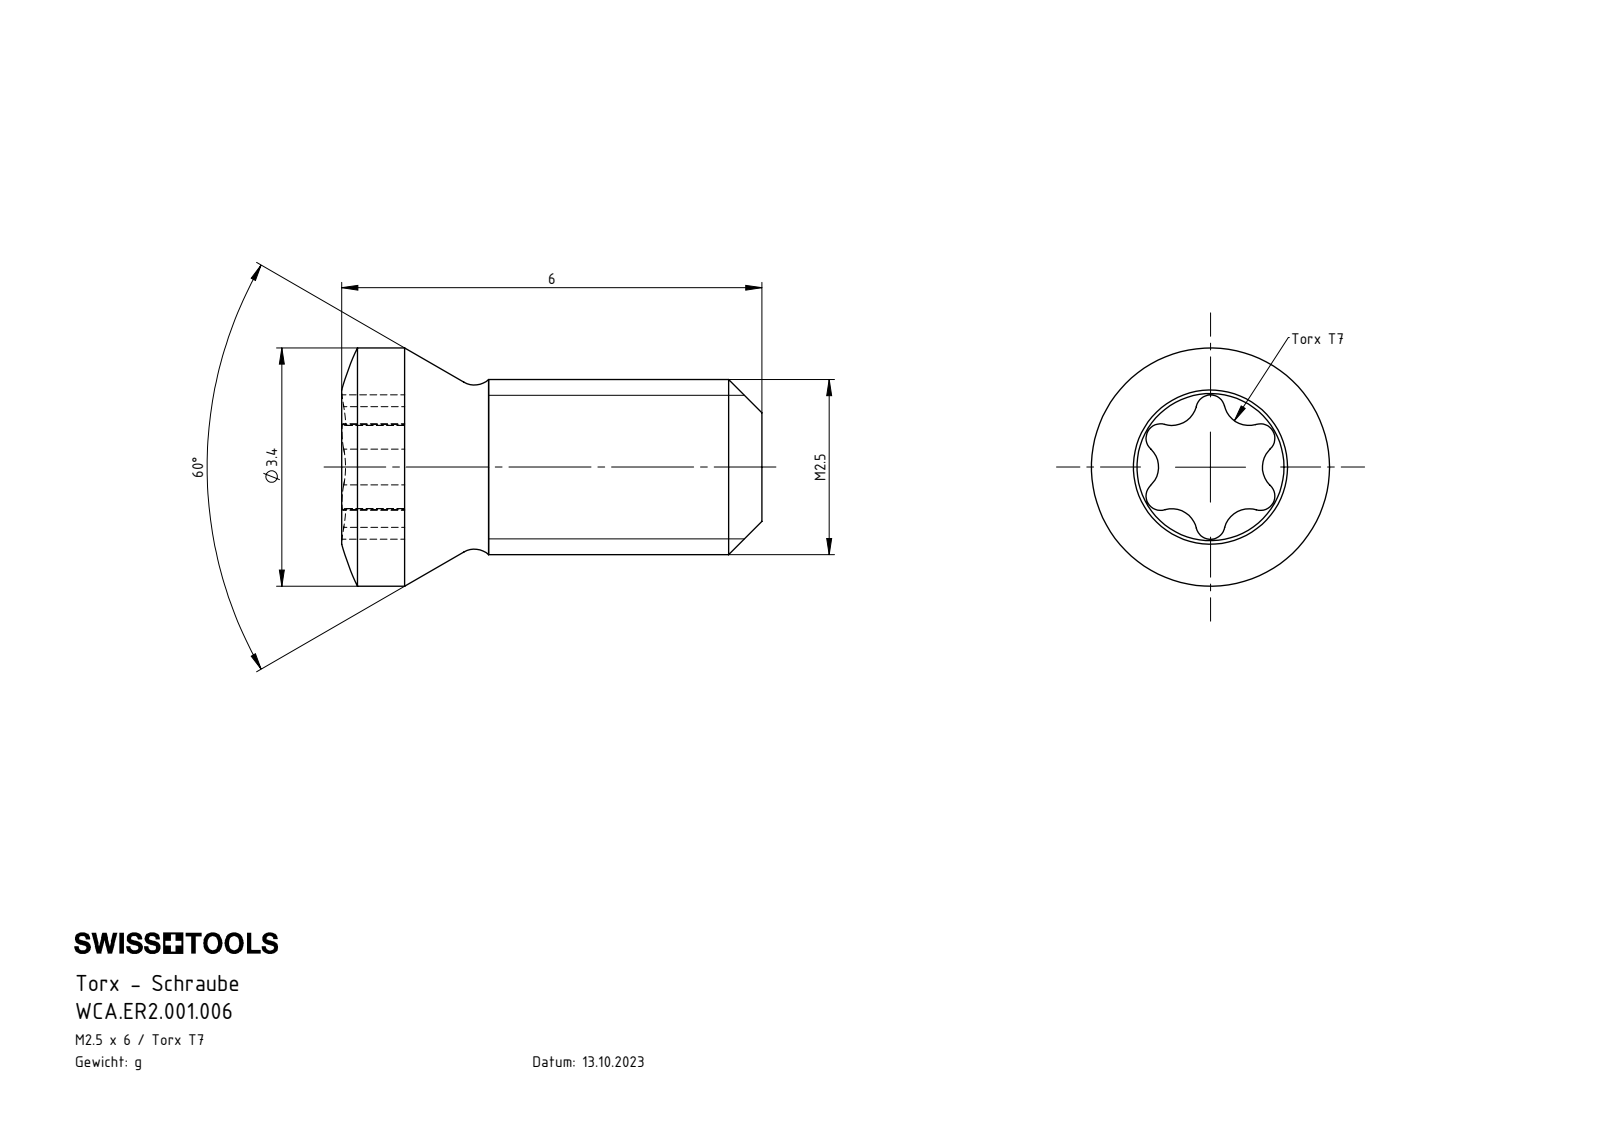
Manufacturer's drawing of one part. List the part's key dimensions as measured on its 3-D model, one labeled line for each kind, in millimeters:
Part name (STEP PRODUCT): WCA.ER2.001.006
STEP written by: SolidWorks 2017 (AUTOMOTIVE_DESIGN)
Units: millimetres
Bodies: 1 solid, 34 faces (3 planar, 19 cylindrical, 12 other)
Overall size (bounding box): 6 × 3.4 × 3.4
Volume: 31 mm³ · Surface area: 67 mm²
Round bosses / shafts (diameter × count): ⌀3.4 ×1, ⌀2.5 ×1
Partial cylindrical surfaces — rounded edges, fillets, slot ends (radius × count): R0.21 ×6, R0.36 ×5, R0.36 ×1
Main face-to-face distances: 5.1, 0.9, 6
